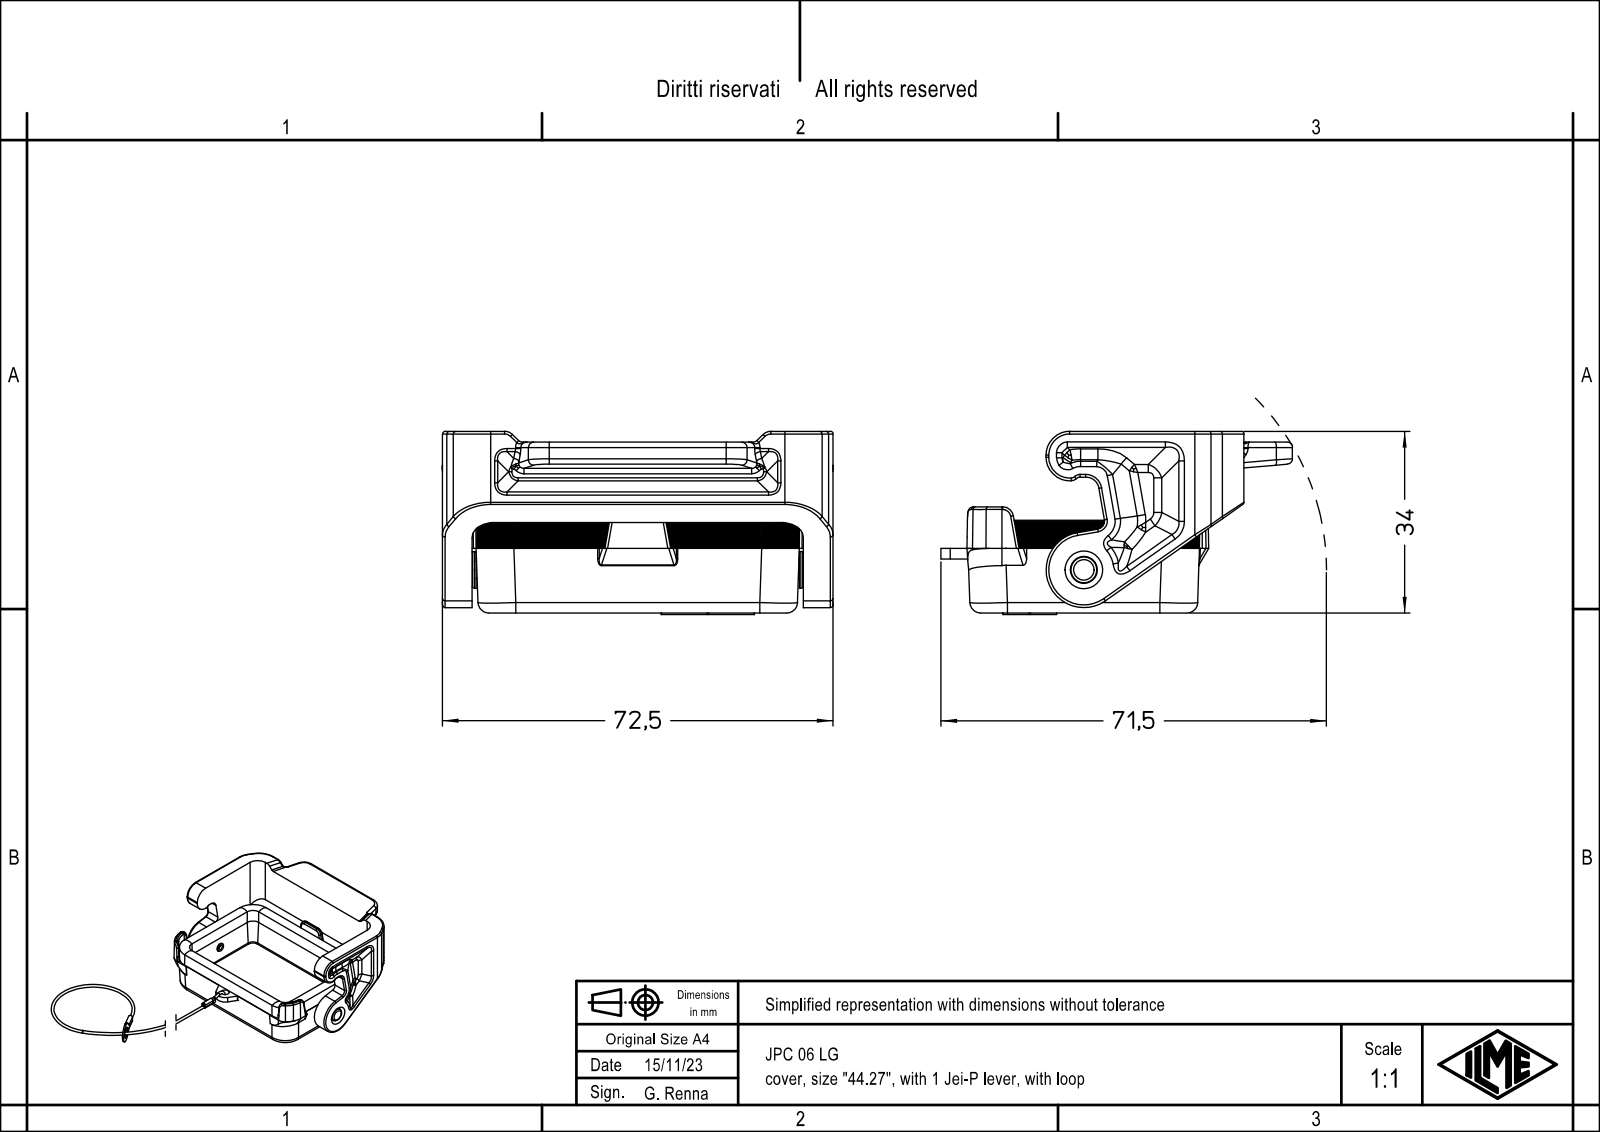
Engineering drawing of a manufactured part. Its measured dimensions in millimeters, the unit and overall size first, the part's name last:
Units: millimetres
Overall size (bounding box): 72.58 × 65.25 × 34
Round holes (diameter × count): ⌀3 ×1
Round bosses / shafts (diameter × count): ⌀6.8 ×1, ⌀4.8 ×1
Partial cylindrical surfaces — rounded edges, fillets, slot ends (radius × count): R0.5 ×29, R1 ×21, R2 ×21, R3 ×16, R0.33 ×15, R1.5 ×10, R7 ×9, R6 ×6
Main face-to-face distances: 2.5, 61.5, 31.7, 29.2, 4, 5.5, 67, 2, 33.7, 31.2
Volume: 30 190 mm³ · Surface area: 18 419 mm²
Bodies: 1 solid, 534 faces (139 planar, 169 cylindrical, 226 other)
Part name (STEP PRODUCT): JPC 06 LG
STEP written by: Creo Elements/Direct Modeling 20.1B 02-Apr-2019 (C) Parametric Technology GmbH (AUTOMOTIVE_DESIGN)
